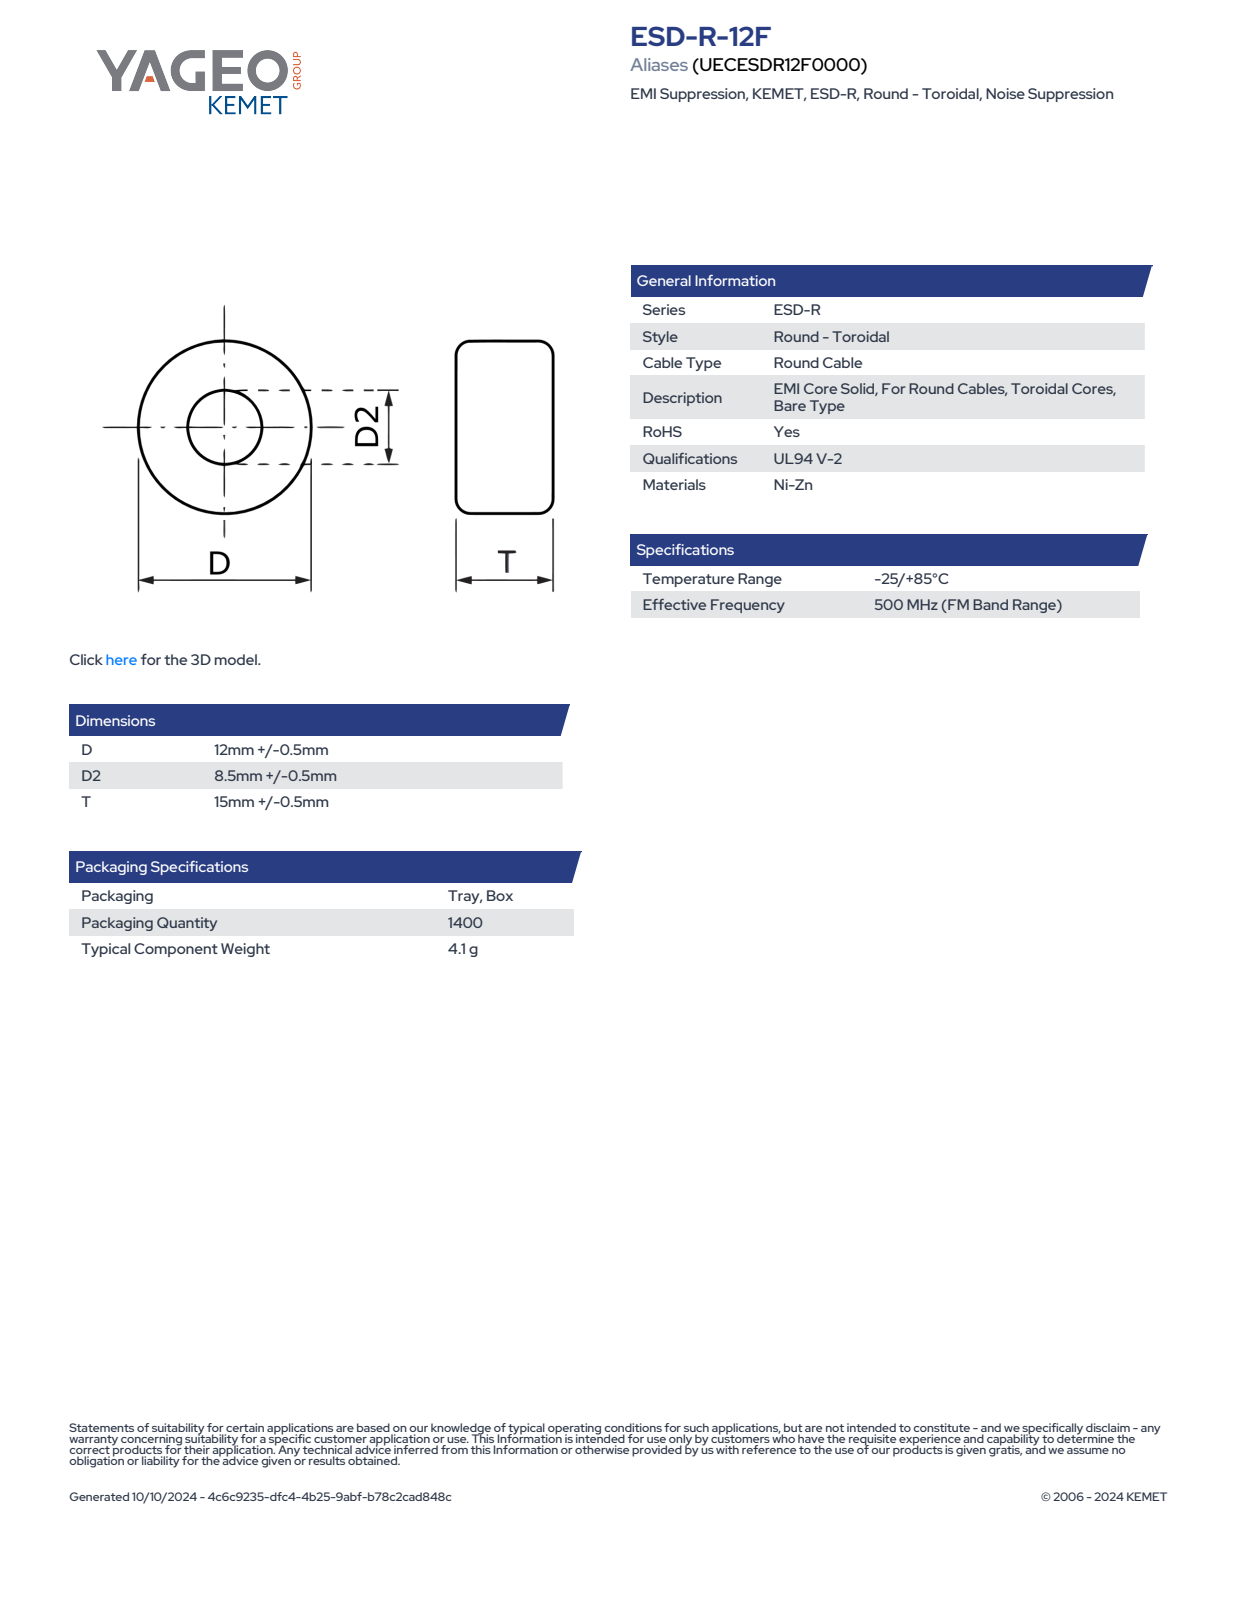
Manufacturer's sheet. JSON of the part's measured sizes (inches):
{"part_name": "EC_KBC_D12.5D28.5T15.5", "step_written_by": "SolidWorks 2021 (AUTOMOTIVE_DESIGN)", "units": "inches", "bodies": {"solids": 1, "faces": 66, "planar": 24, "cylindrical": 7, "other": 35}, "overall_size": [0.61, 0.493, 0.492], "volume_in3": 0.062, "surface_area_in2": 1.772, "round_holes": [[0.335, 1]], "round_bosses_or_shafts": [[0.492, 1]], "partial_cylinders_radius": [[0.246, 1]], "face_to_face_distances": [0.61, 0.272, 0.339, 0.067, 0.013, 0.284, 0.326, 0.054, 0.042, 0.313]}
